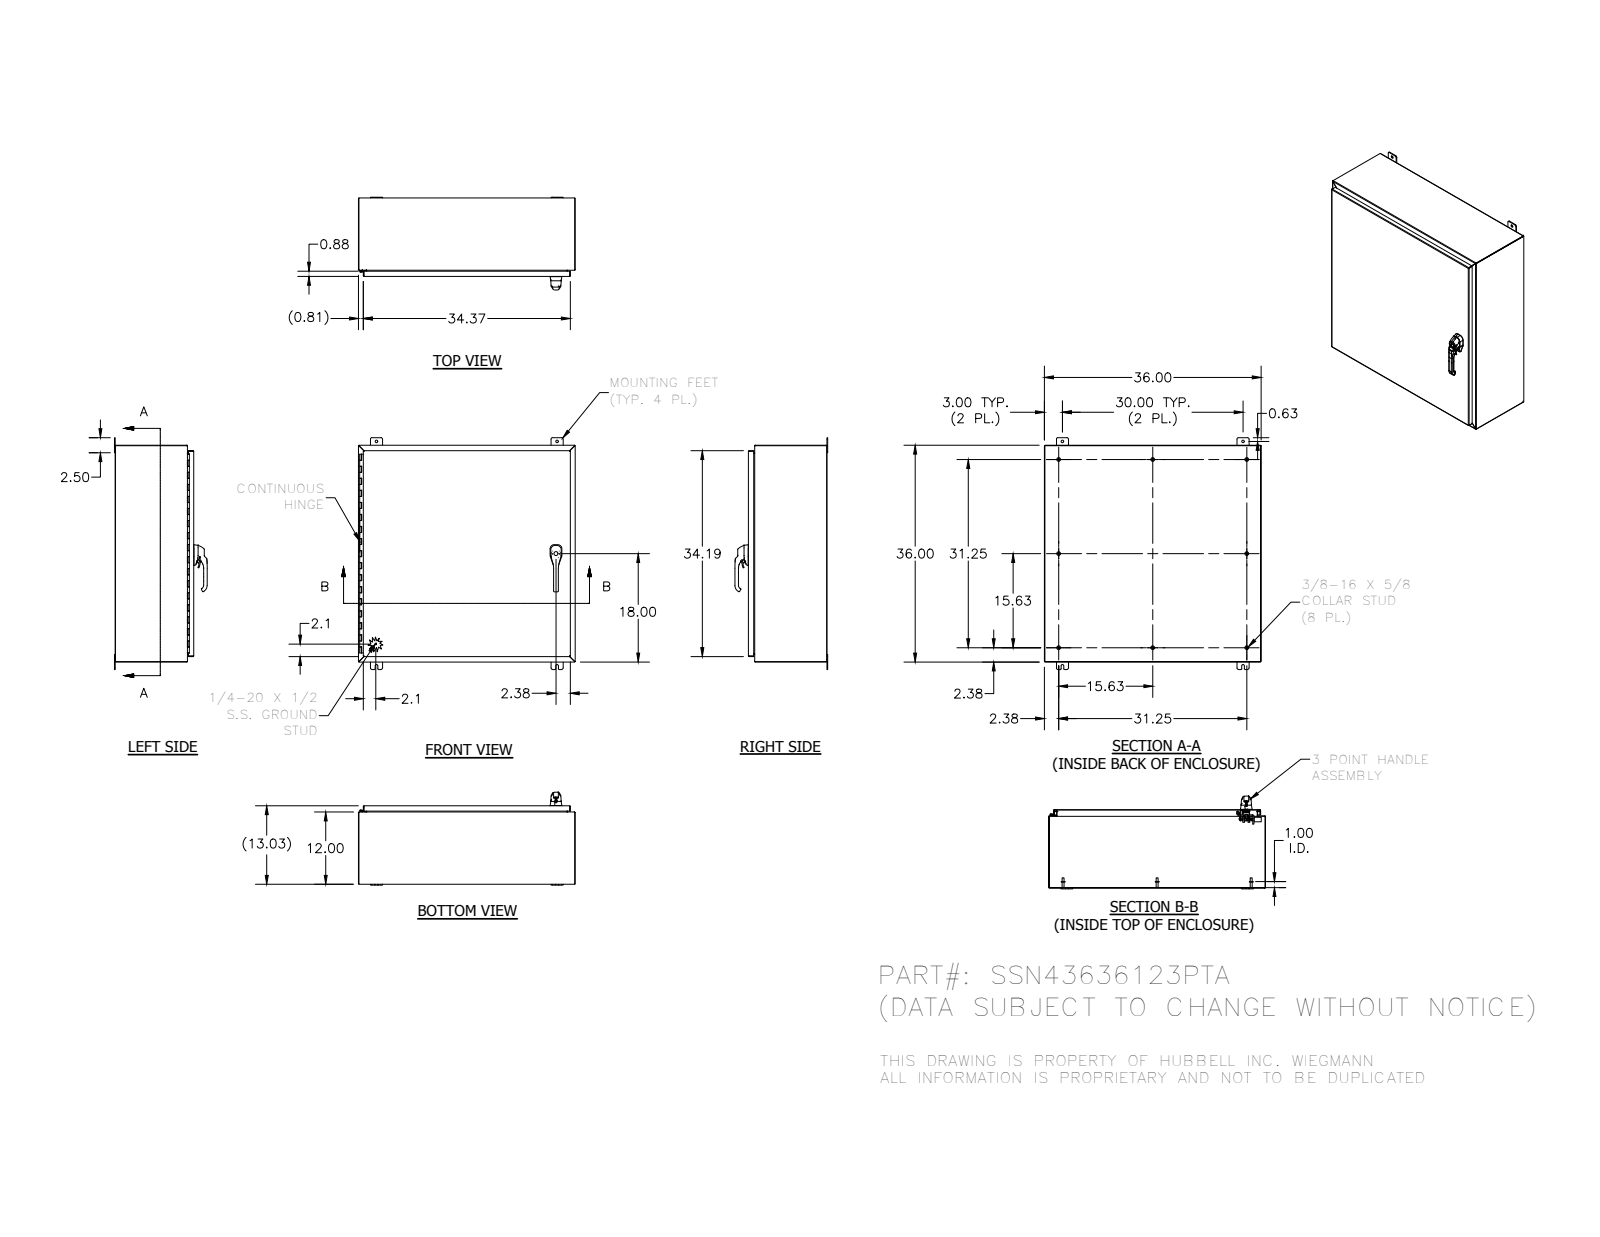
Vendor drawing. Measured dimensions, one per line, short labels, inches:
name: HFW3762; HFW369101; 1091-75; 32874-36 (+8 more)
written by: SolidWorks 2014 (AUTOMOTIVE_DESIGN)
unit: in
bodies: 62 solids, 3213 faces (1120 planar, 1308 cylindrical, 785 other)
size: 38.5 × 36 × 15.408
volume: 377.1 in³; area: 9 899 in²
holes: 8× ⌀0.262, 4× ⌀0.187, 4× ⌀0.438, 3× ⌀0.213, 3× ⌀0.281, 2× ⌀0.241, 2× ⌀0.25, 2× ⌀0.252, 2× ⌀0.315, 2× ⌀0.4, 2× ⌀0.402, 2× ⌀0.413
bosses: 8× ⌀0.625, 8× ⌀0.33, 3× ⌀0.236, 2× ⌀1, 2× ⌀0.563, 2× ⌀0.533, 2× ⌀0.531, 2× ⌀0.5
rounds: 172× R0.02, 113× R0.012, 26× R0.125, 22× R0.031, 21× R0.019, 20× R0.25, 18× R0.105, 15× R0.05
face distances: 0.074, 12.959, 35.926, 12.885, 13.033, 35.852, 36, 11.926, 1.033, 12
hole spacings: 0.38, 0.492, 0.76, 0.886, 26.428, 0.234, 0.258, 0.38
